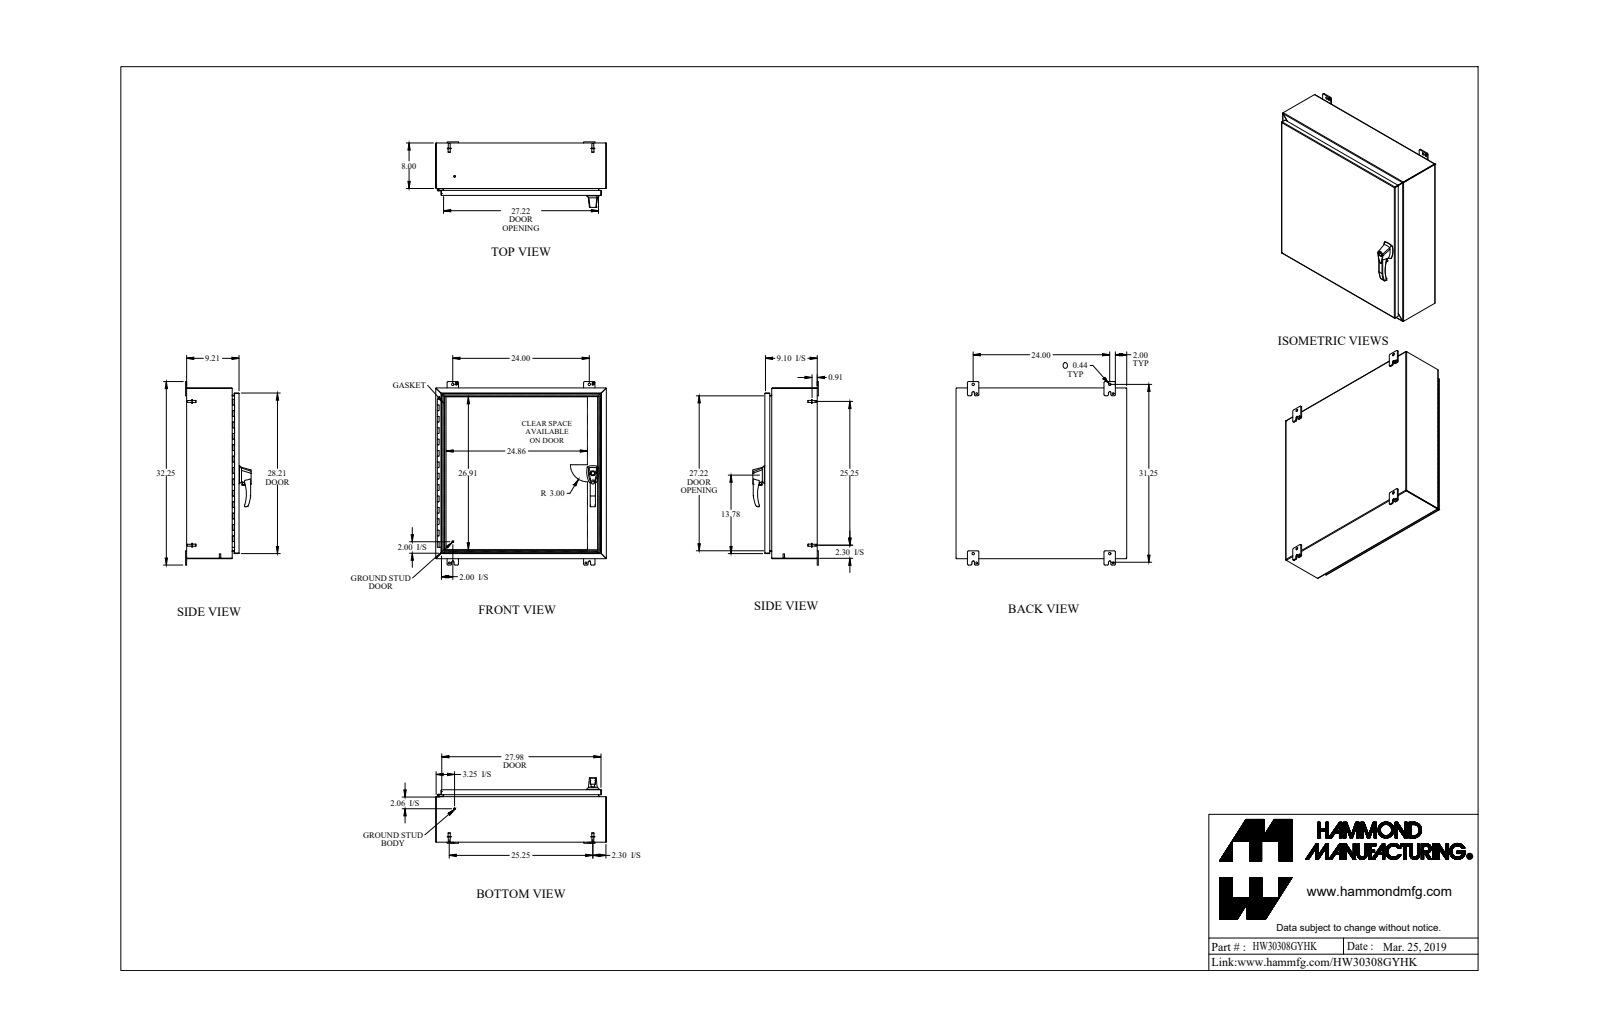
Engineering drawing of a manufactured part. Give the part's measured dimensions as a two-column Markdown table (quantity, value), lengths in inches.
| quantity | value |
| --- | --- |
| part name | HW30308GYHK |
| STEP written by | SolidWorks 2018 (AUTOMOTIVE_DESIGN) |
| units | inches |
| bodies | 44 solids, 1525 faces (757 planar, 611 cylindrical, 157 other) |
| overall size | 32.25 × 30 × 11.512 |
| volume | 271.9 in³ |
| surface area | 7 109 in² |
| round holes (diameter × count) | 0.176 × 6, 0.25 × 4, 0.313 × 4, 0.196 × 3, 0.265 × 3, 0.413 × 3, 0.256 × 2, 0.394 × 2, 0.437 × 2, 0.187 × 1, 0.233 × 1, 0.334 × 1 |
| round bosses / shafts (diameter × count) | 0.375 × 9, 0.25 × 6, 0.156 × 6, 0.65 × 4, 0.33 × 4, 1 × 3, 0.63 × 2, 0.51 × 2 |
| partial cylindrical surfaces (radius × count) | 0.188 × 36, 0.25 × 27, 0.036 × 20, 0.108 × 20, 0.06 × 12, 0.116 × 12, 0.125 × 9, 0.045 × 8 |
| main face-to-face distances | 0.072, 0.072, 29.928, 9.138, 9.066, 9.21, 9.138, 29.856, 30, 7.928 |
| hole center spacings | 11.118, 11.119, 22.237, 1.111, 11.119, 24, 24.721, 28.895 |
